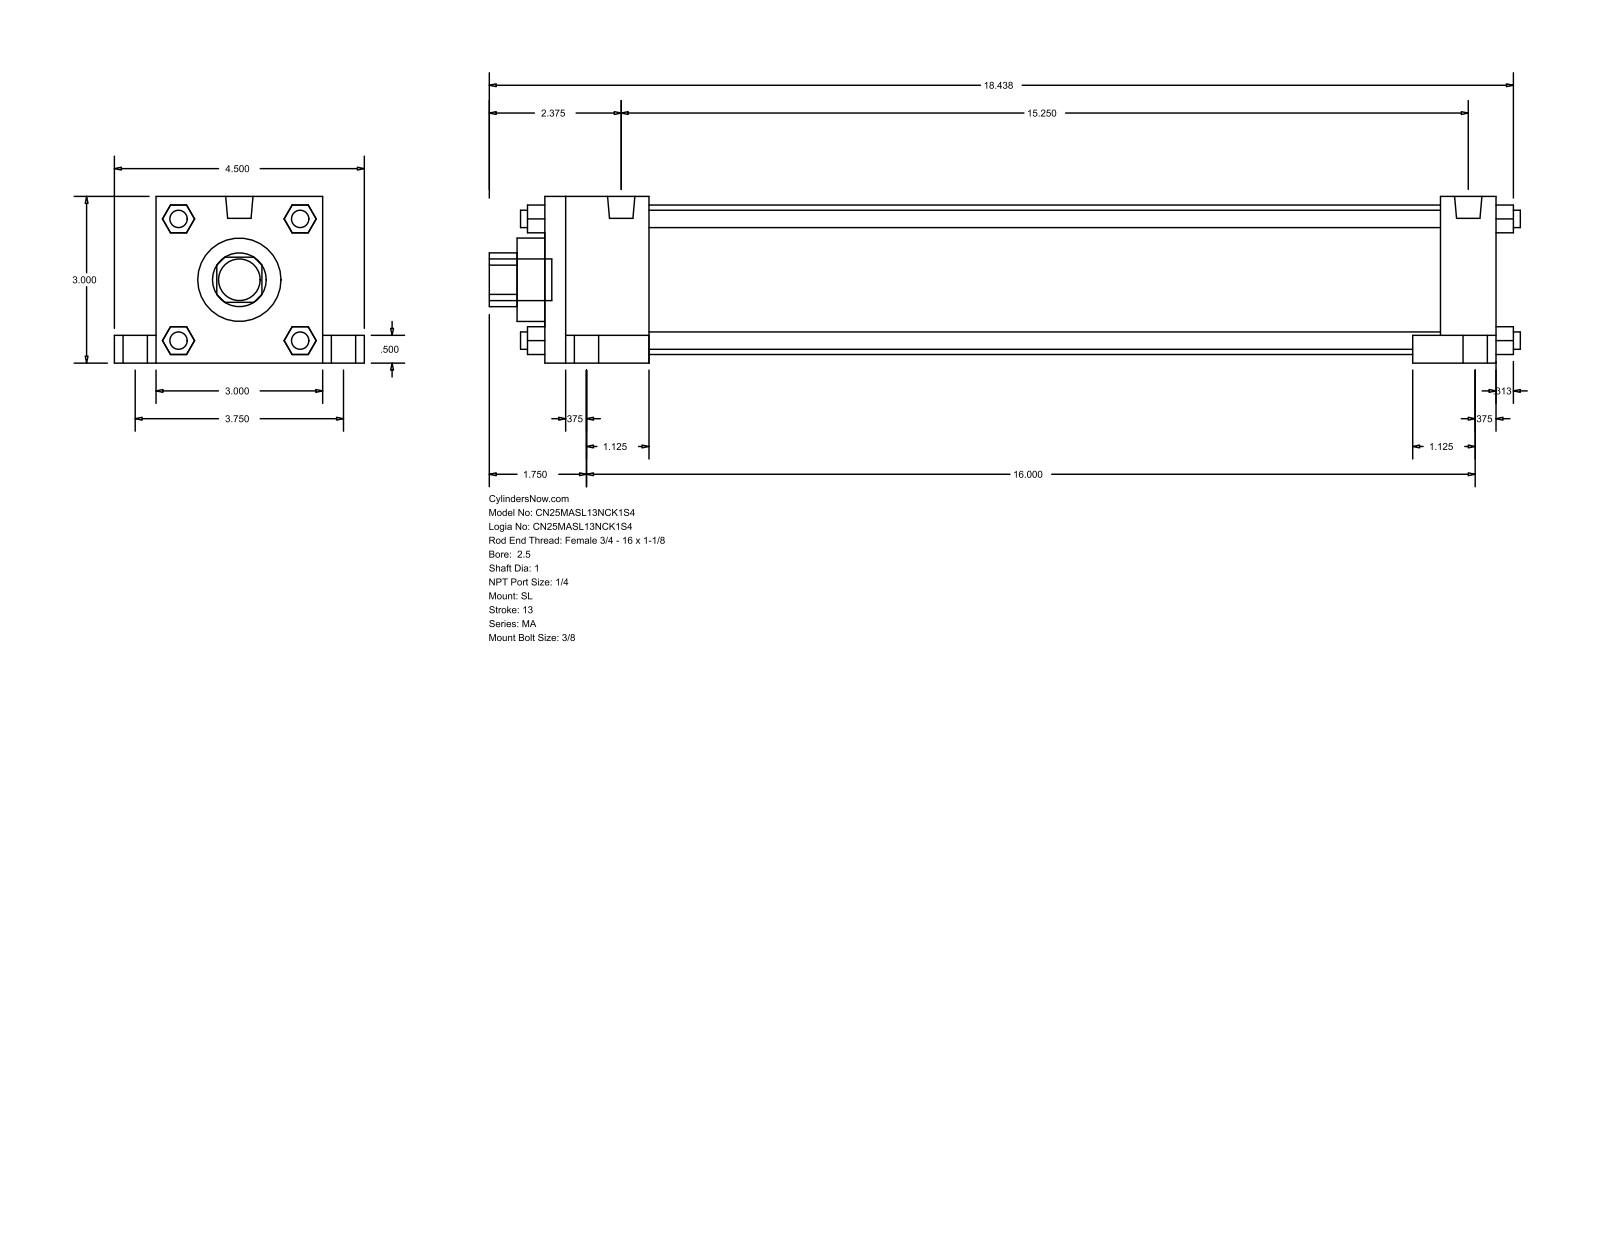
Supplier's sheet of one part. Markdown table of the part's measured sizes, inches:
| quantity | value |
| --- | --- |
| part name | MA_SL__0250_1 |
| STEP written by | GSSL Pune (CONFIG_CONTROL_DESIGN) |
| units | inches |
| bodies | 0 solids, 148 faces (112 planar, 36 cylindrical, 0 other) |
| overall size | 18.563 × 4.5 × 3 |
| round holes (diameter × count) | 1 × 1, 1.5 × 1, 2.69 × 1 |
| round bosses / shafts (diameter × count) | 0.313 × 8, 0.687 × 4, 0.437 × 4, 0.492 × 2, 0.75 × 1 |
| partial cylindrical surfaces (radius × count) | 0.484 × 1 |
| main face-to-face distances | 3, 17.125, 0.5, 14.25, 1, 1.875, 15.25, 16.125, 0.75, 3.75 |
